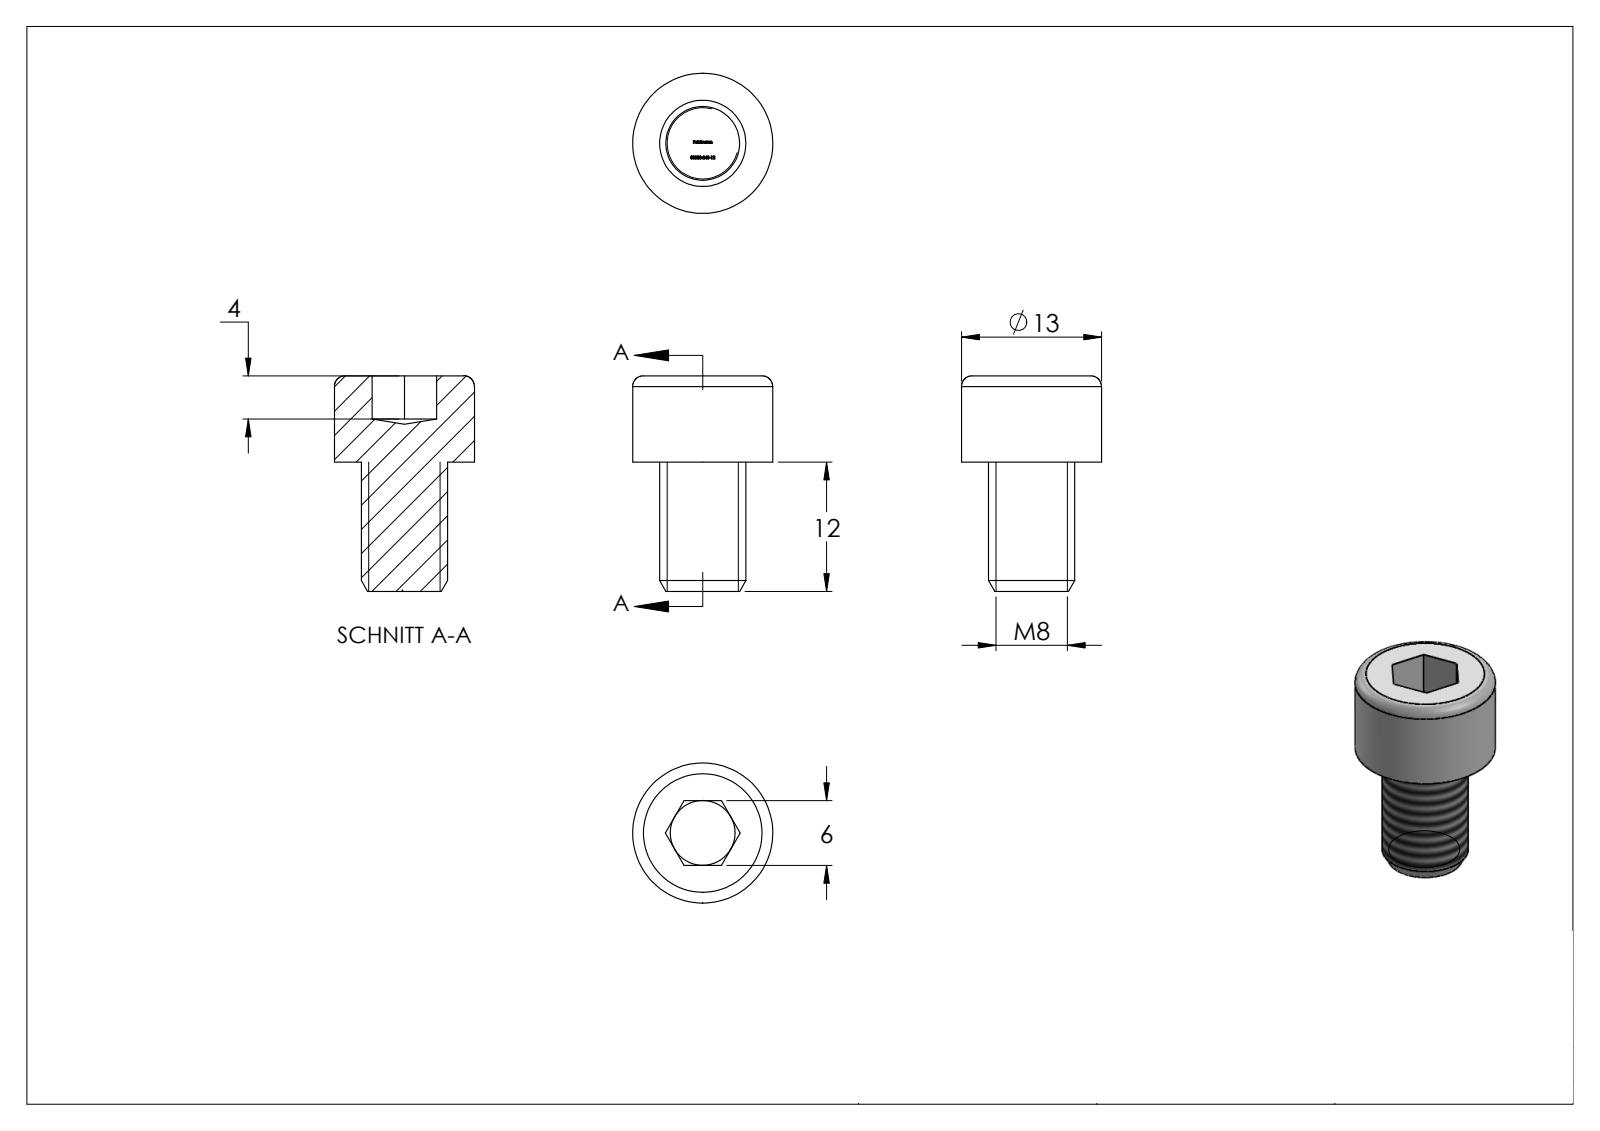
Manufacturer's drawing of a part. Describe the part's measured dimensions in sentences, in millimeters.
The part is named "58333-240-12". Its 3-D file was written by "SolidWorks 2015 (CONFIG_CONTROL_DESIGN)". It is 1 solid with 291 faces: 150 planar, 2 cylindrical and 139 other. Overall it measures 21 by 13 by 13 millimeters. Its volume is 1 520 cubic millimeters and its surface area 950 square millimeters. Round bosses or shafts: 1 of diameter 13, 1 of diameter 8. The main face-to-face distances are 8, 6, 12, 20, 4, 16, 11.9, 15.9, 19.9, 0.33.
